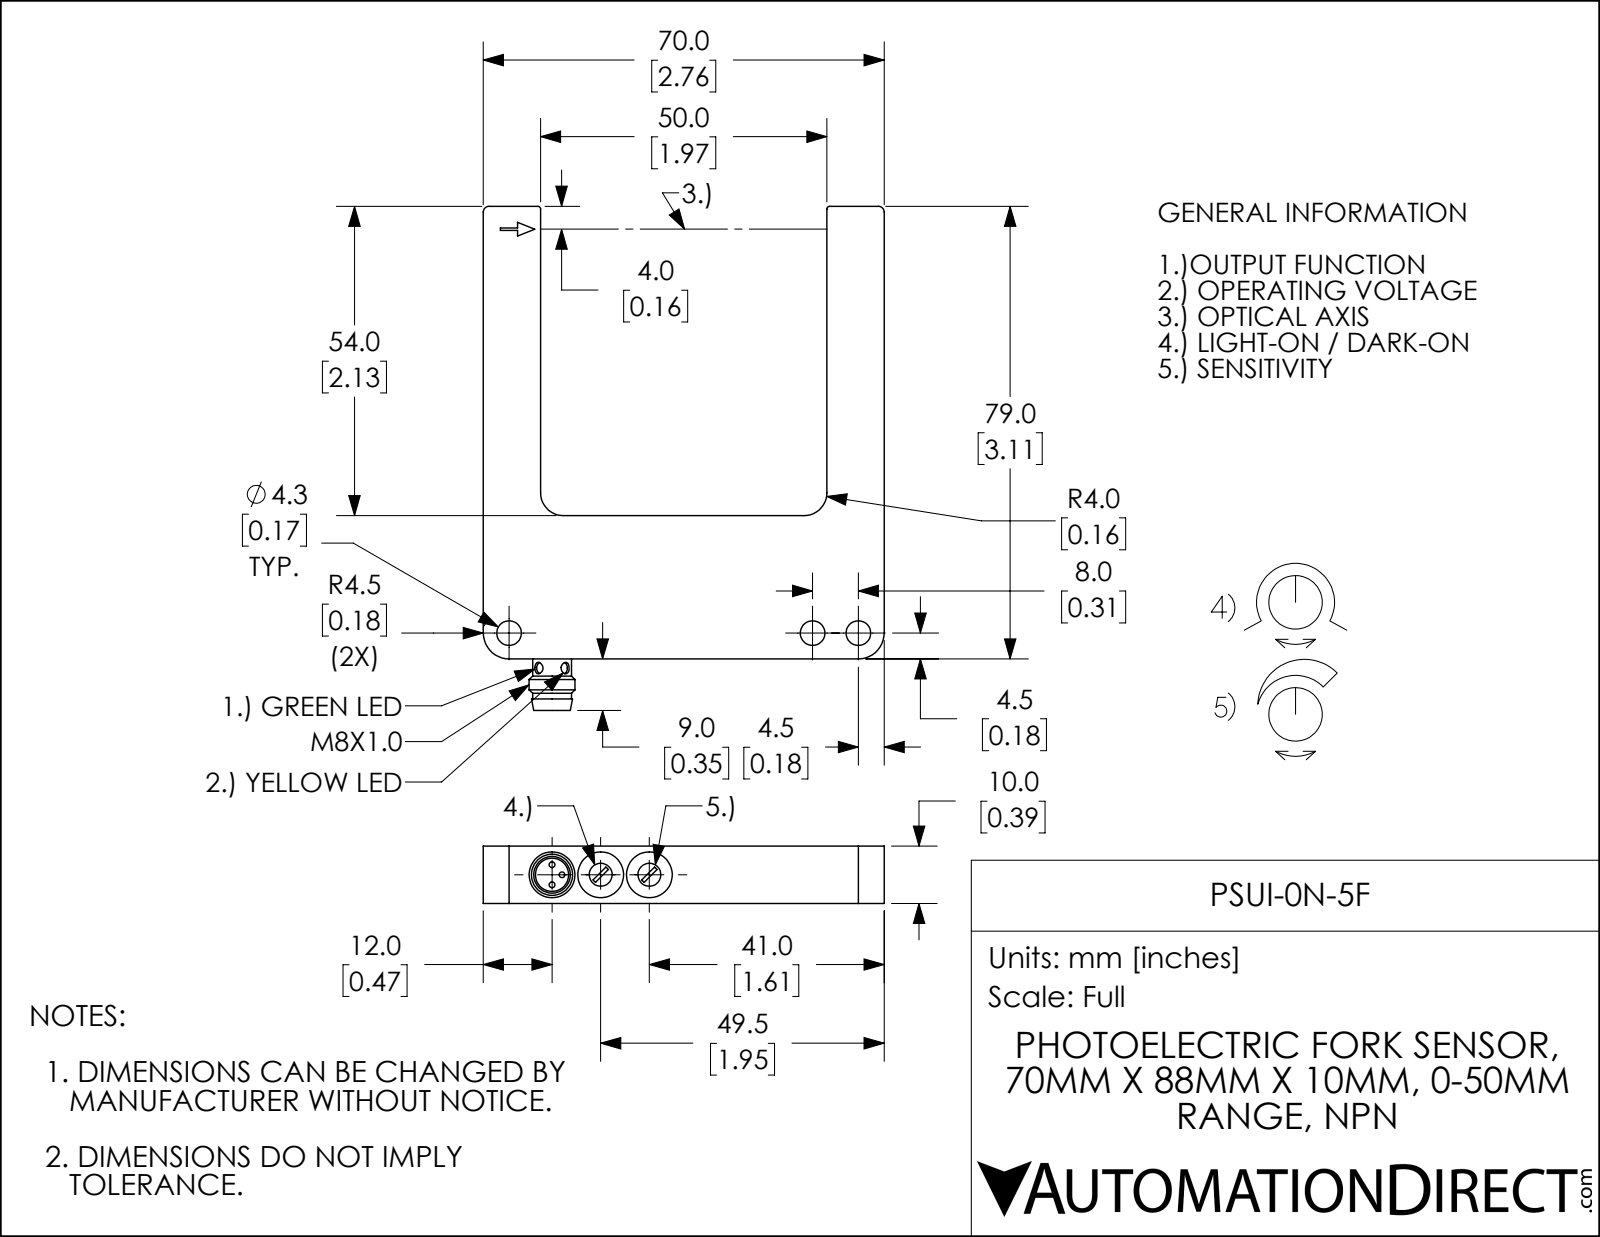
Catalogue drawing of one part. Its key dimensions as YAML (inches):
part_name: "PSUI-0N-5F"
step_written_by: "SolidWorks 2017 (AUTOMOTIVE_DESIGN)"
units: inches
bodies: {solids: 1, faces: 71, planar: 35, cylindrical: 30, other: 6}
overall_size: [3.465, 2.756, 0.394]
volume: 1.712
surface_area: 16
round_holes:
  - {diameter: 0.169, count: 3}
  - {diameter: 0.079, count: 2}
  - {diameter: 0.157, count: 2}
  - {diameter: 0.315, count: 2}
  - {diameter: 0.228, count: 1}
round_bosses_or_shafts:
  - {diameter: 0.039, count: 3}
  - {diameter: 0.315, count: 1}
  - {diameter: 0.267, count: 1}
partial_cylinders:
  - {radius: 0.02, count: 2}
  - {radius: 0.039, count: 2}
  - {radius: 0.063, count: 2}
  - {radius: 0.157, count: 2}
  - {radius: 0.177, count: 2}
face_to_face_distances: [0.394, 2.362, 2.756, 1.969, 0.984, 2.126, 3.11, 3.106, 0.98, 0.157]
hole_center_spacings: [0.335, 0.315, 0.669, 2.087, 2.402]
